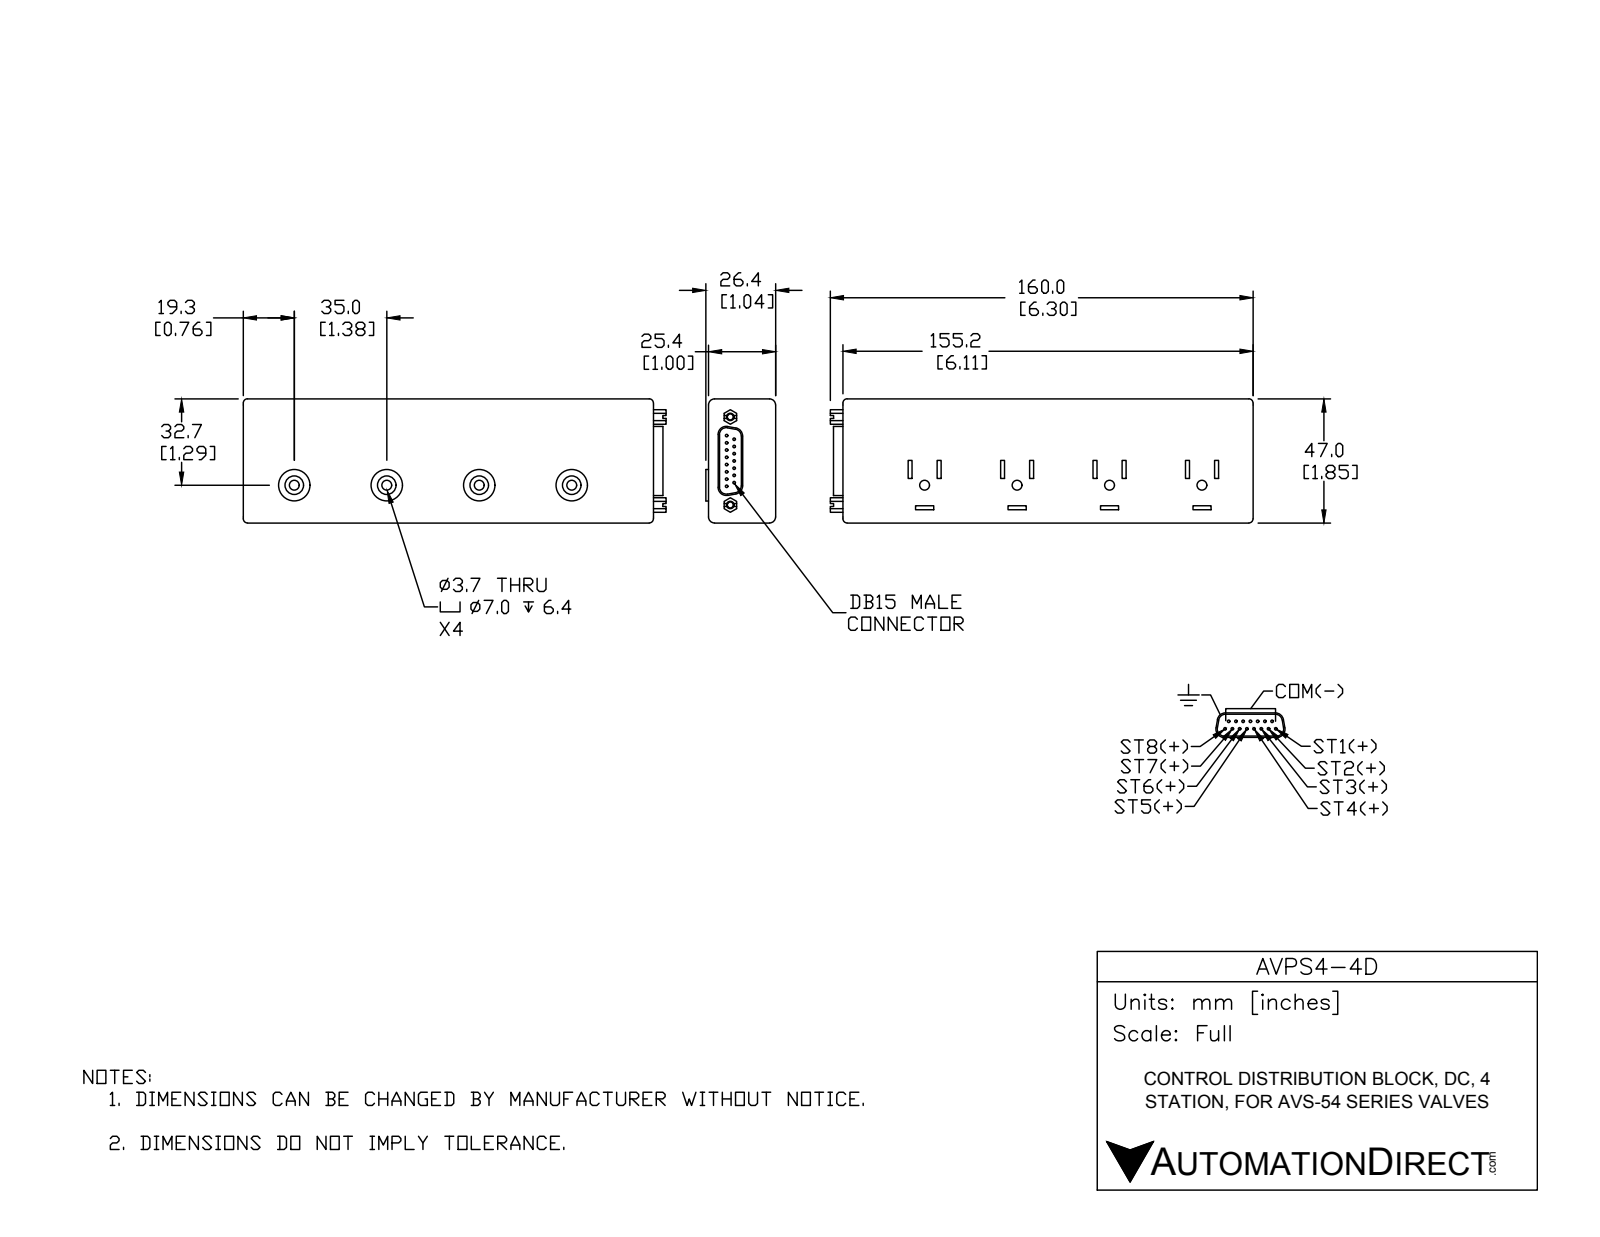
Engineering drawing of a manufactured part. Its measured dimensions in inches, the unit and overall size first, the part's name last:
Units: inches
Overall size (bounding box): 6.301 × 1.85 × 1.04
Round holes (diameter × count): ⌀0.145 ×4, ⌀0.275 ×4, ⌀0.089 ×2
Round bosses / shafts (diameter × count): ⌀0.039 ×15, ⌀0.469 ×4
Partial cylindrical surfaces — rounded edges, fillets, slot ends (radius × count): R0.062 ×8, R0.09 ×4, R0.102 ×4, R0.122 ×4
Main face-to-face distances: 1, 1.85, 6.112, 1.378, 0.059, 0.433, 0.04, 1.04, 2.756, 1.437
Hole centre spacings: 1.378, 1.311, 1.378, 2.756, 2.756, 4.134
Volume: 11.11 in³ · Surface area: 43.41 in²
Bodies: 1 solid, 219 faces (127 planar, 80 cylindrical, 12 other)
Part name (STEP PRODUCT): AVPS4-4D
STEP written by: SolidWorks 2016 (AUTOMOTIVE_DESIGN)
